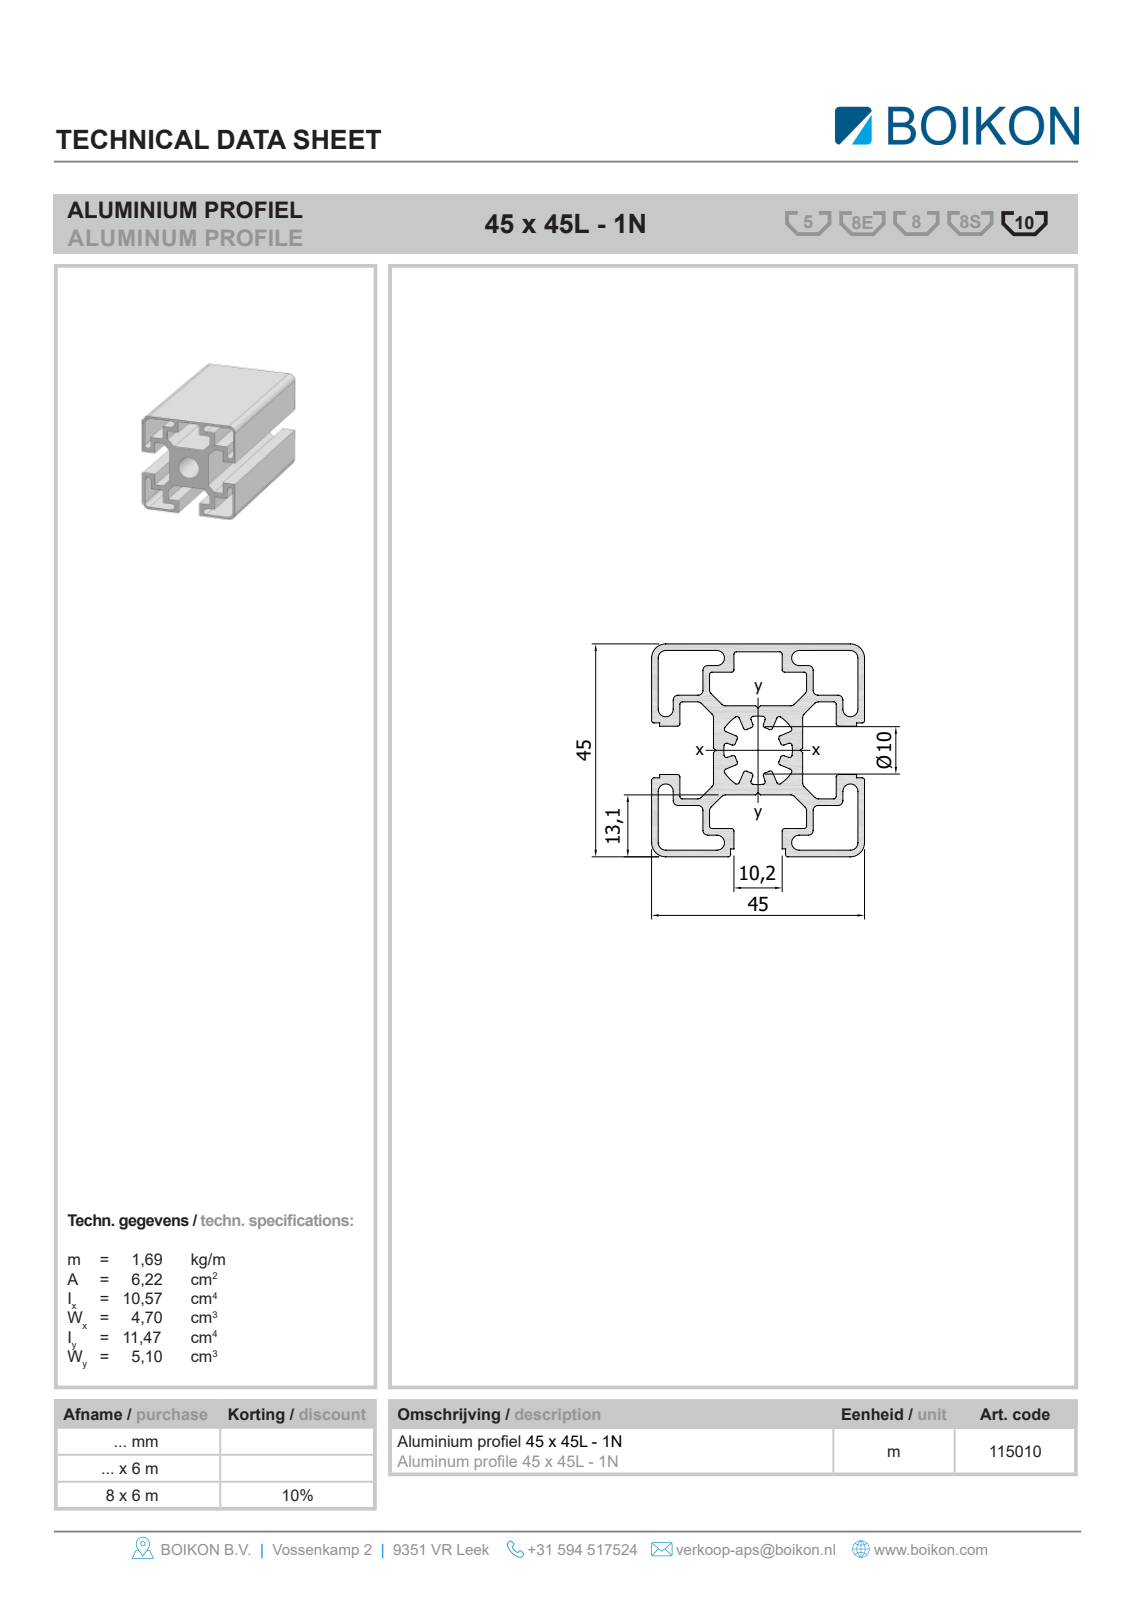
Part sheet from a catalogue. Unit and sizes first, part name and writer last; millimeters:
Units: millimetres
Overall size (bounding box): 1000 × 45 × 45
Round holes (diameter × count): ⌀10 ×1
Partial cylindrical surfaces — rounded edges, fillets, slot ends (radius × count): R2 ×4, R3 ×4
Main face-to-face distances: 35, 10, 1, 44, 9, 34, 45, 13.1, 31.9, 3.1
Volume: 839 808 mm³ · Surface area: 539 584 mm²
Bodies: 1 solid, 71 faces (62 planar, 9 cylindrical, 0 other)
Part name (STEP PRODUCT): Root; 11501045x45L-1NBOIKON0
STEP written by: HiCAD 2013 1802.4 Build 509 (AUTOMOTIVE_DESIGN)
